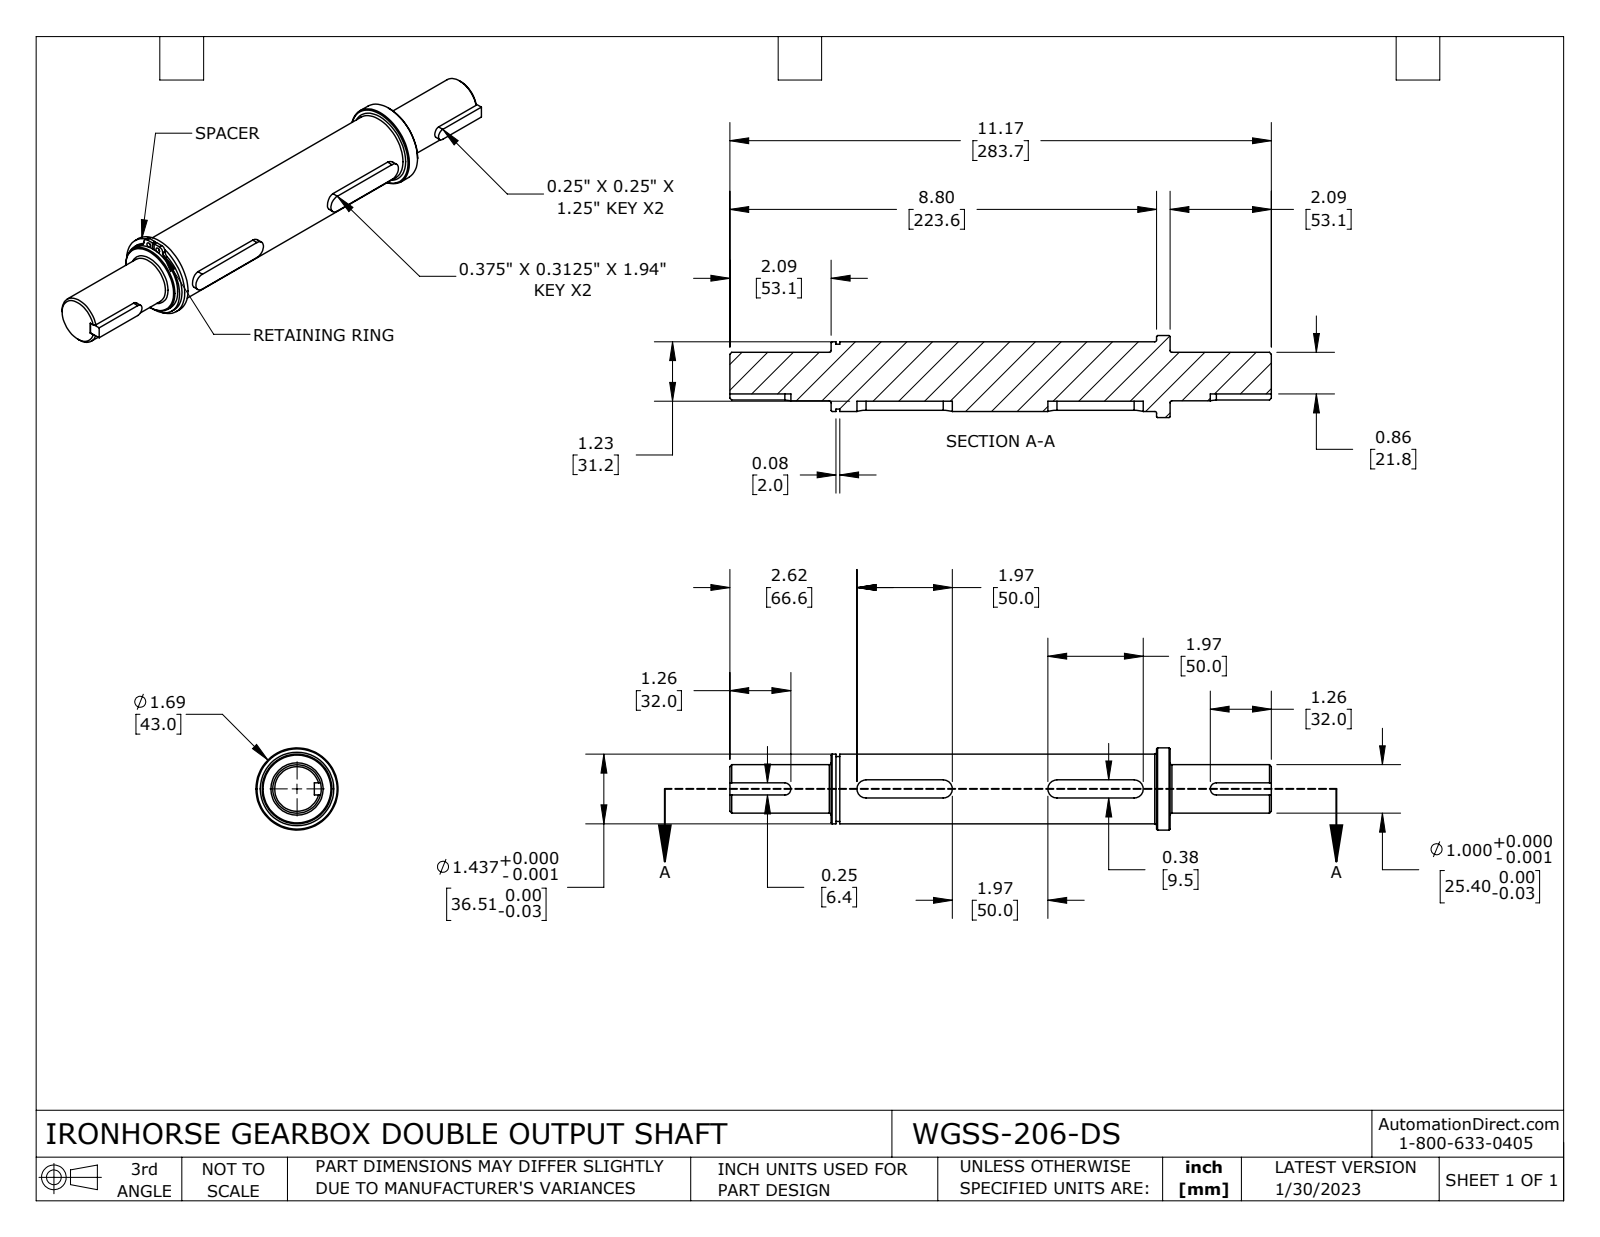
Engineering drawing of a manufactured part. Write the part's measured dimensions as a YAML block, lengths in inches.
part_name: "WGSS-206-DS"
step_written_by: "SolidWorks 2021 (CONFIG_CONTROL_DESIGN)"
units: inches
bodies: {solids: 7, faces: 111, planar: 47, cylindrical: 49, other: 15}
overall_size: [11.169, 1.707, 1.693]
volume: 15.1
surface_area: 63.84
round_holes:
  - {diameter: 0.106, count: 2}
  - {diameter: 1.303, count: 1}
  - {diameter: 1.441, count: 1}
round_bosses_or_shafts:
  - {diameter: 1.693, count: 1}
  - {diameter: 1.535, count: 1}
  - {diameter: 1.437, count: 1}
  - {diameter: 1.339, count: 1}
  - {diameter: 1, count: 1}
partial_cylinders:
  - {radius: 0.1, count: 4}
  - {radius: 0.188, count: 4}
  - {radius: 0.188, count: 3}
  - {radius: 0.125, count: 2}
  - {radius: 0.187, count: 1}
face_to_face_distances: [0.313, 0.063, 0.312, 2.09, 9.078, 6.811, 0.149, 0.461, 0.063, 0.375]
hole_center_spacings: [0.763, 0.264]
